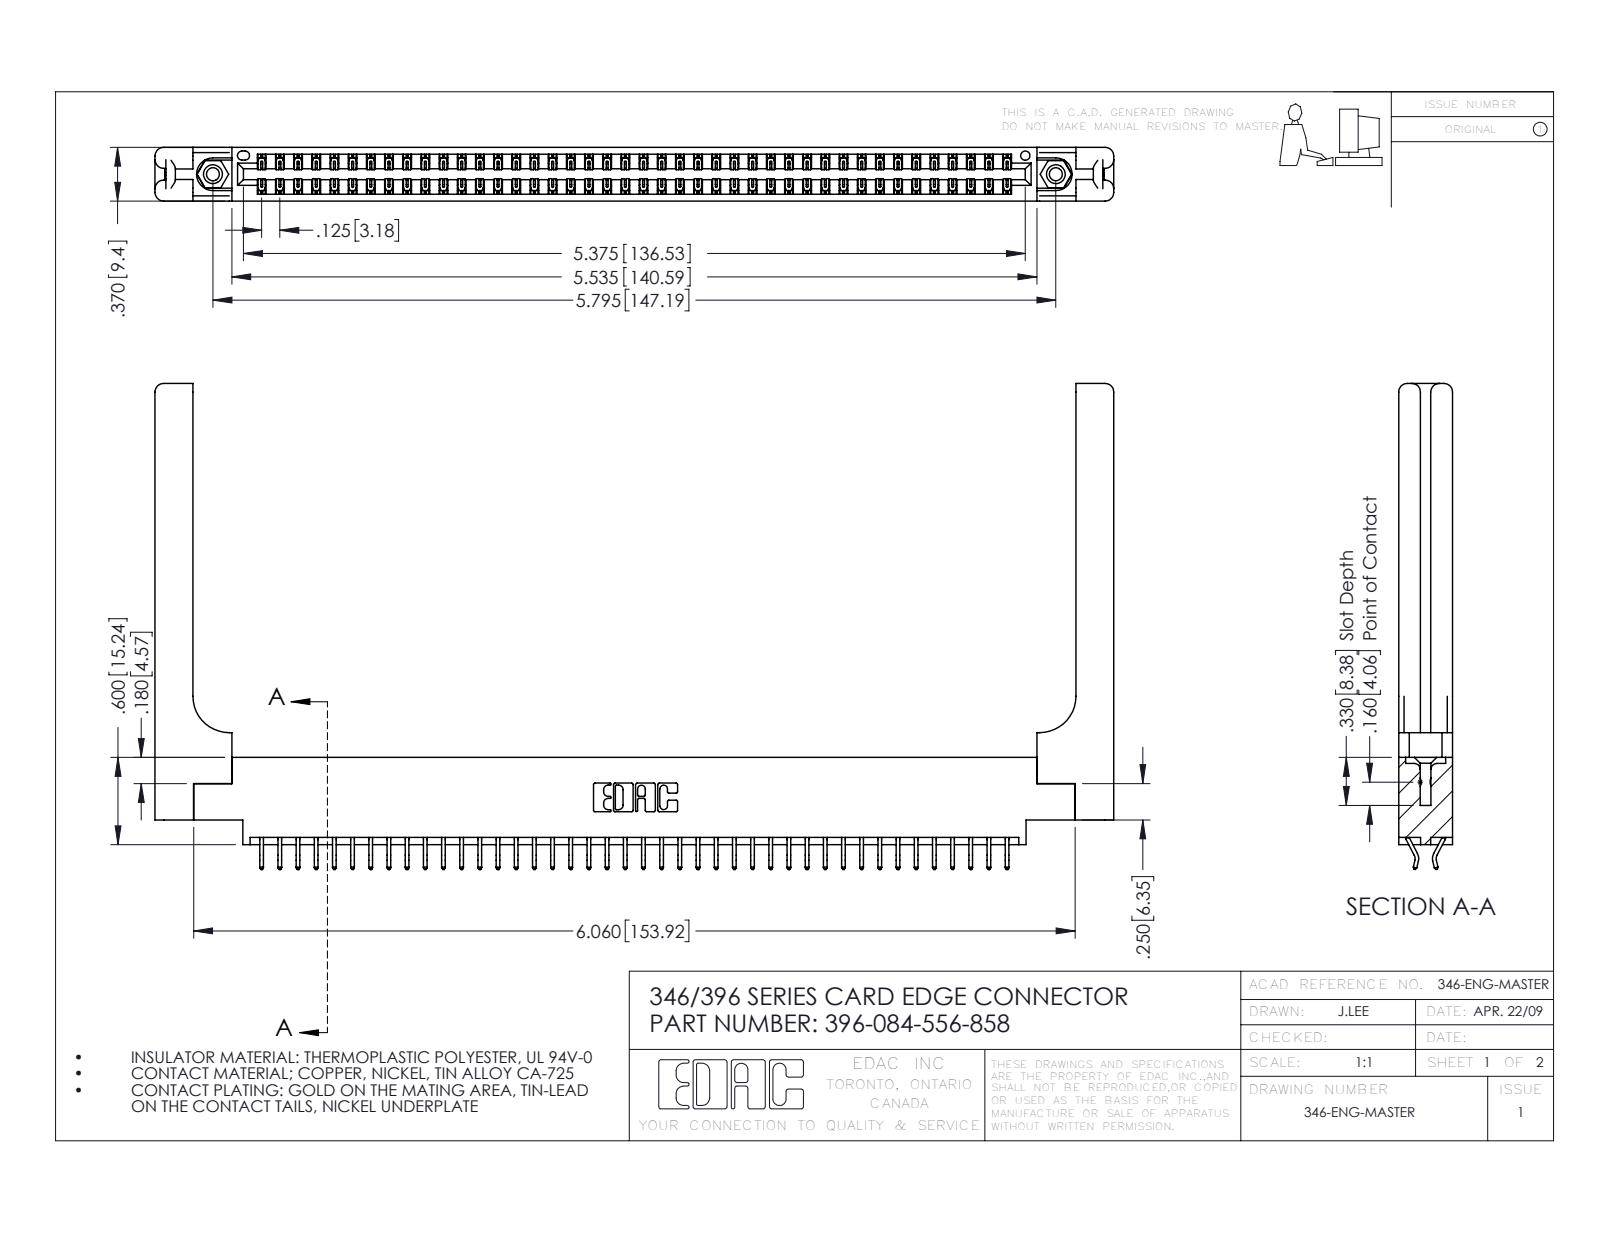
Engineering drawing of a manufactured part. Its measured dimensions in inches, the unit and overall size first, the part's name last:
Units: inches
Overall size (bounding box): 6.591 × 3.34 × 0.37
Round holes (diameter × count): ⌀0.089 ×2, ⌀0.125 ×2, ⌀0.156 ×2, ⌀0.064 ×1
Round bosses / shafts (diameter × count): ⌀0.155 ×2
Partial cylindrical surfaces — rounded edges, fillets, slot ends (radius × count): R0.006 ×126, R0.01 ×22, R0.06 ×16, R0.007 ×6, R0.031 ×6, R0.026 ×3, R0.01 ×2, R0.014 ×2
Main face-to-face distances: 0.37, 0.048, 0.322, 0.072, 0.148, 0.15, 0.25, 0.025, 0.298, 0.275
Hole centre spacings: 0.246, 5.586, 5.795
Volume: 1.444 in³ · Surface area: 42.31 in²
Bodies: 89 solids, 5254 faces (3504 planar, 1690 cylindrical, 60 other)
Part name (STEP PRODUCT): 345-292-001_556 Tail; 346 Part_0.170 Offset - 0.156 Dia-TH; 345-250-001_345-250-001-102; 396-084-556-858 (+1 more)
STEP written by: SolidWorks 2016 (CONFIG_CONTROL_DESIGN)
